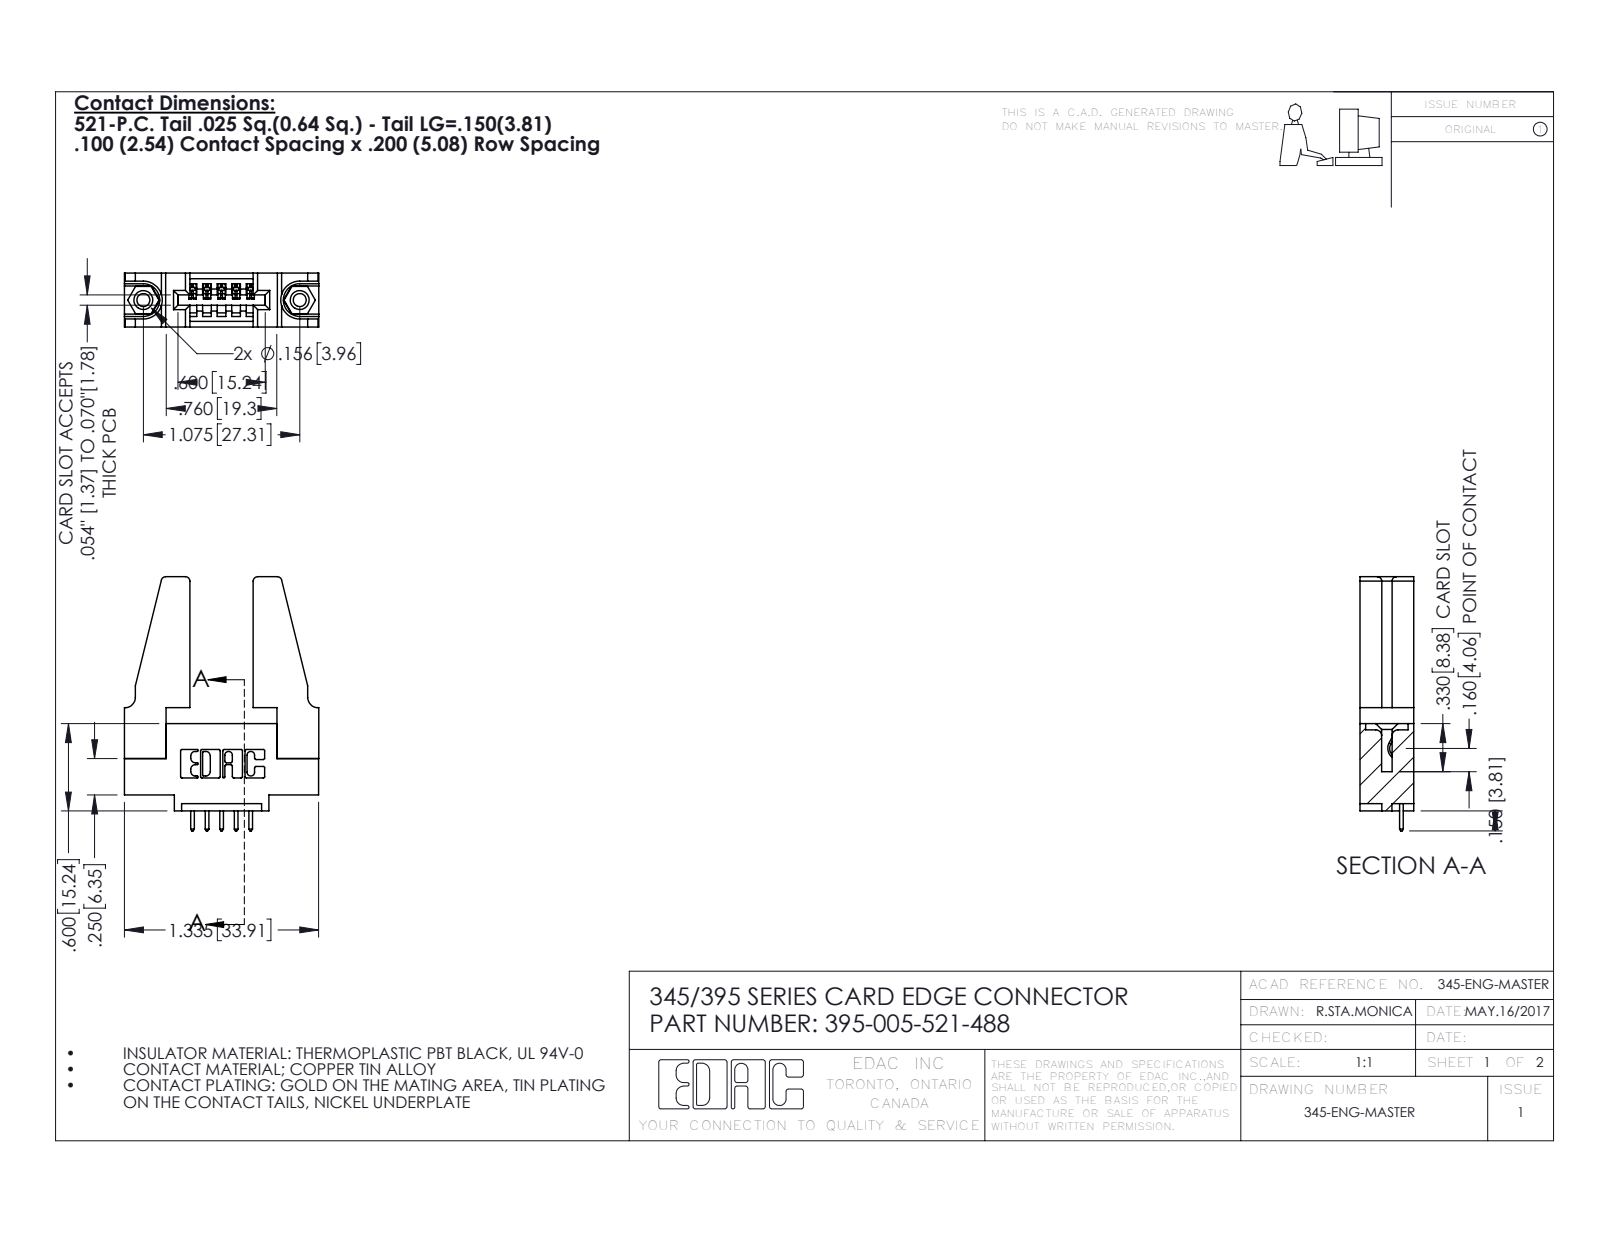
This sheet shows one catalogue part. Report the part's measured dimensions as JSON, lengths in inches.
{"part_name": "345-292-001_345-293-121; 345-250-001_345-250-001-102; 345 Part_0.110 Offset - 0.156 Dia-TH; 395-005-521-488 (+1 more)", "step_written_by": "SolidWorks 2016 (CONFIG_CONTROL_DESIGN)", "units": "inches", "bodies": {"solids": 10, "faces": 544, "planar": 356, "cylindrical": 172, "other": 16}, "overall_size": [1.747, 1.336, 0.37], "volume_in3": 0.371, "surface_area_in2": 9.946, "round_holes": [[0.089, 2], [0.125, 2], [0.156, 2], [0.064, 1]], "round_bosses_or_shafts": [[0.155, 2]], "partial_cylinders_radius": [[0.01, 22], [0.006, 10], [0.01, 10], [0.03, 8], [0.007, 6], [0.031, 6], [0.026, 3], [0.031, 2]], "face_to_face_distances": [0.37, 0.072, 0.298, 0.2, 0.148, 0.15, 0.22, 0.077, 0.45, 0.287], "hole_center_spacings": [0.27, 0.847, 1.075]}
